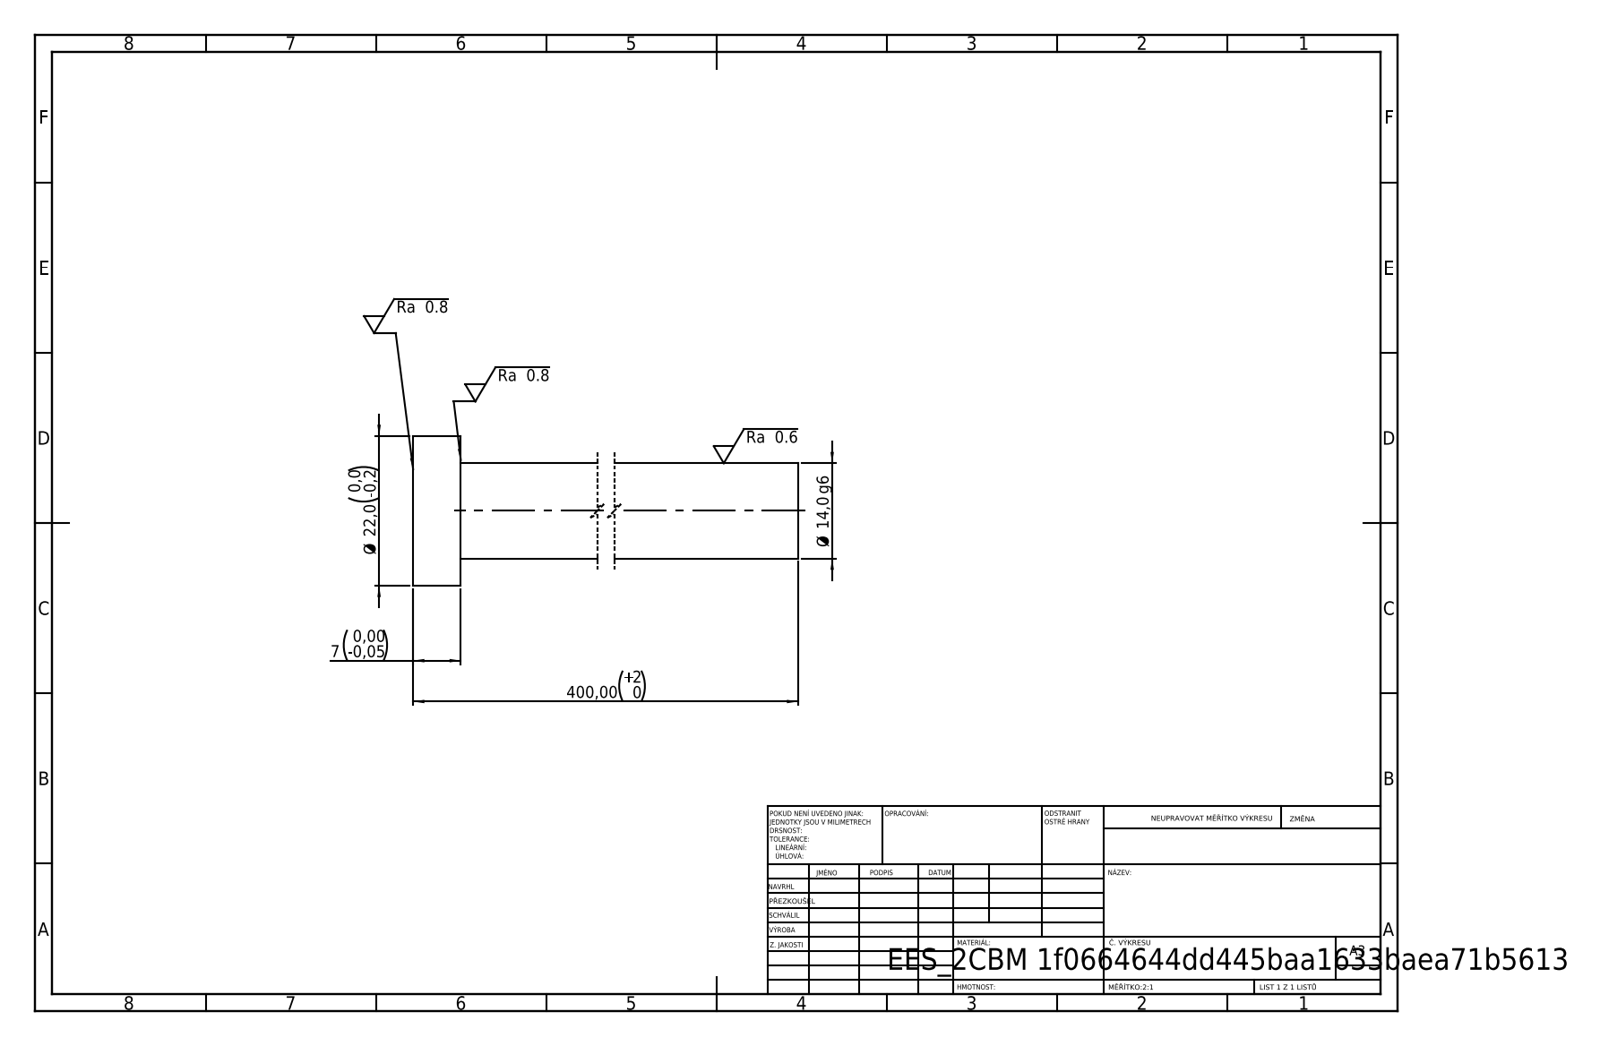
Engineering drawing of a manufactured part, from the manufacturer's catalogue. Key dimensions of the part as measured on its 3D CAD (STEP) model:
STEP written by: SolidWorks 2019 (CONFIG_CONTROL_DESIGN)
Units: millimetres
Bodies: 1 solid, 7 faces (3 planar, 4 cylindrical, 0 other)
Overall size (bounding box): 400 × 22 × 22
Volume: 63 159 mm³ · Surface area: 18 529 mm²
Round bosses / shafts (diameter × count): ⌀22 ×1, ⌀14 ×1
Main face-to-face distances: 7, 400, 393
